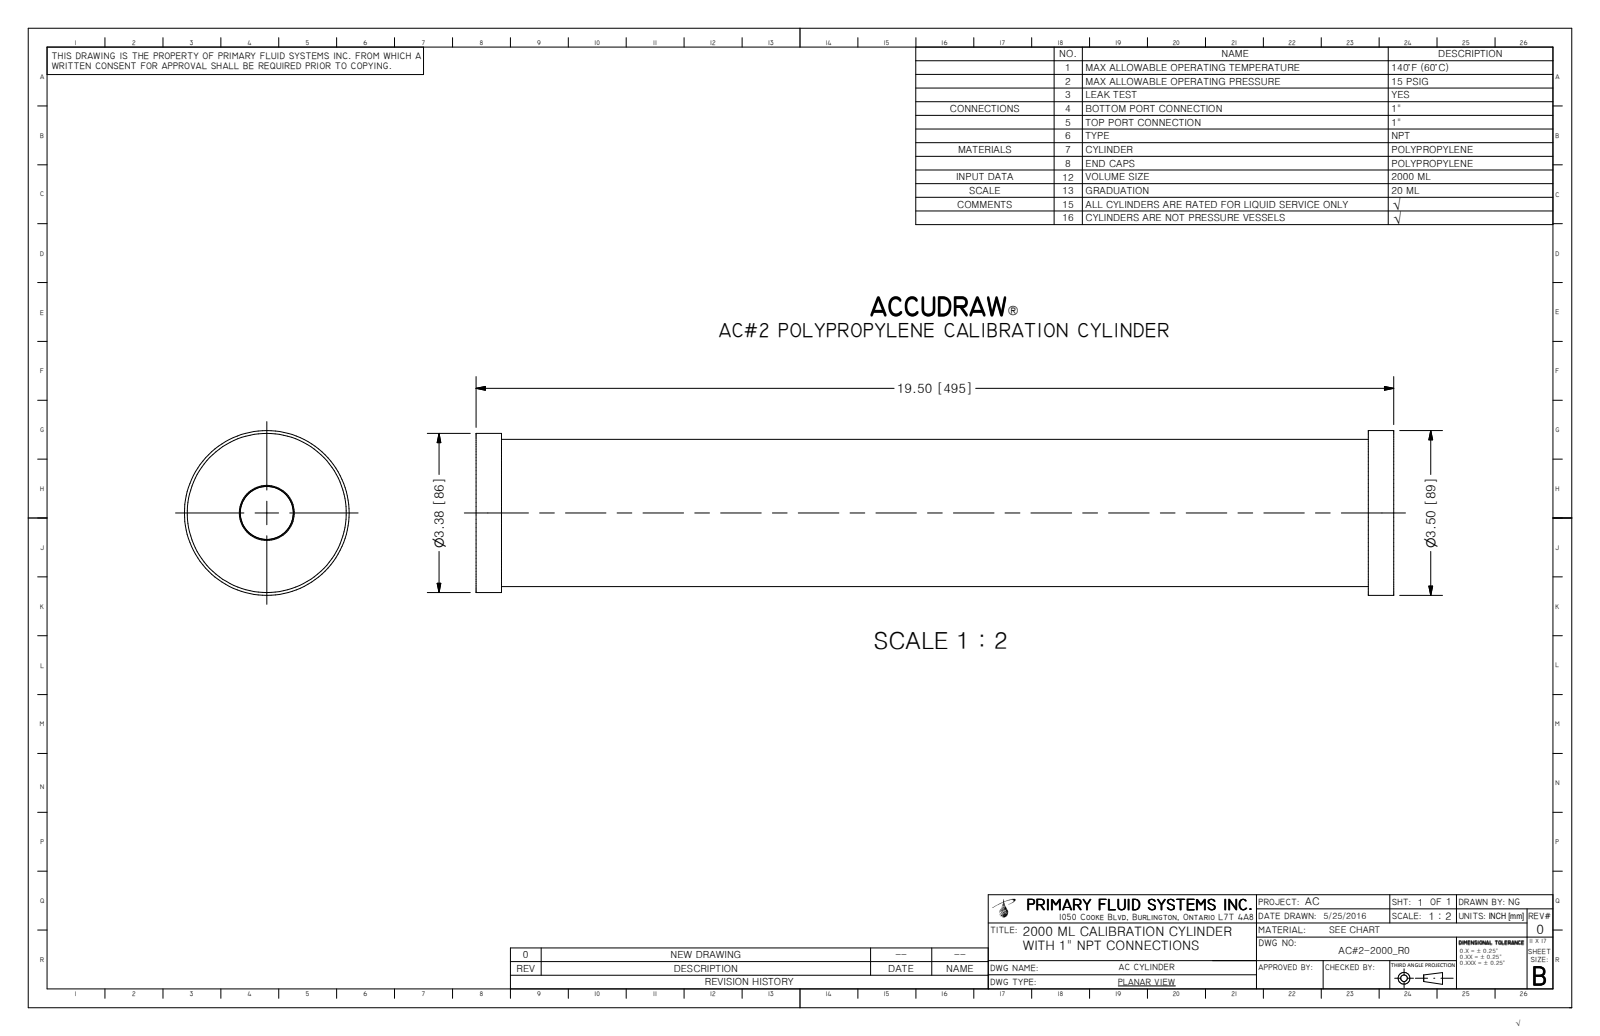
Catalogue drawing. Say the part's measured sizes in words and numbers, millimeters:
The part is named "AC#2-2000_R0; AC-2B-2000; AC-2000-TUBE; AC-2T-2000". Its 3-D file was written by "Autodesk Inventor 2009 (AUTOMOTIVE_DESIGN)". It is 3 solids with 20 faces: 8 planar, 6 cylindrical and 6 other. Overall it measures 495.3 by 88.9 by 88.9 millimeters. Its volume is 363 500 cubic millimeters and its surface area 264 500 square millimeters. Round holes: 1 of diameter 76.3. Round bosses or shafts: 1 of diameter 88.9, 1 of diameter 85.9, 1 of diameter 79.4, 1 of diameter 79.2, 1 of diameter 74.9. The main face-to-face distances are 19.1, 476.3, 495.3, 457.2, 13.7, 481.6, 5.3, 462.5, 467.9.
